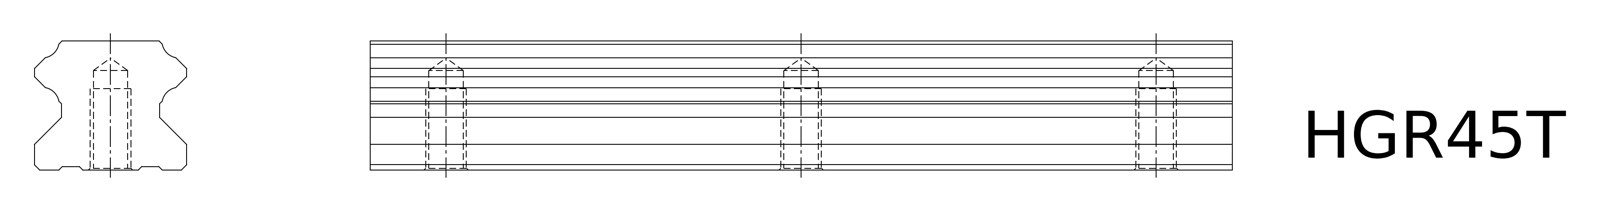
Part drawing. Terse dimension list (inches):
name: HGR45TSLDPRT
written by: SolidWorks 2006104 (CONFIG_CONTROL_DESIGN)
unit: in
bodies: 1 solid, 53 faces (33 planar, 20 cylindrical, 0 other)
size: 10.039 × 1.772 × 1.496
volume: 21.62 in³; area: 76.4 in²
holes: 3× ⌀0.472
rounds: 6× R0.047, 4× R0.031, 4× R0.157
face distances: 1.496, 1.457, 0.624, 0.039, 1.319, 0.696, 1.772, 0.315, 10.039, 2.043
hole spacings: 4.134, 8.268
